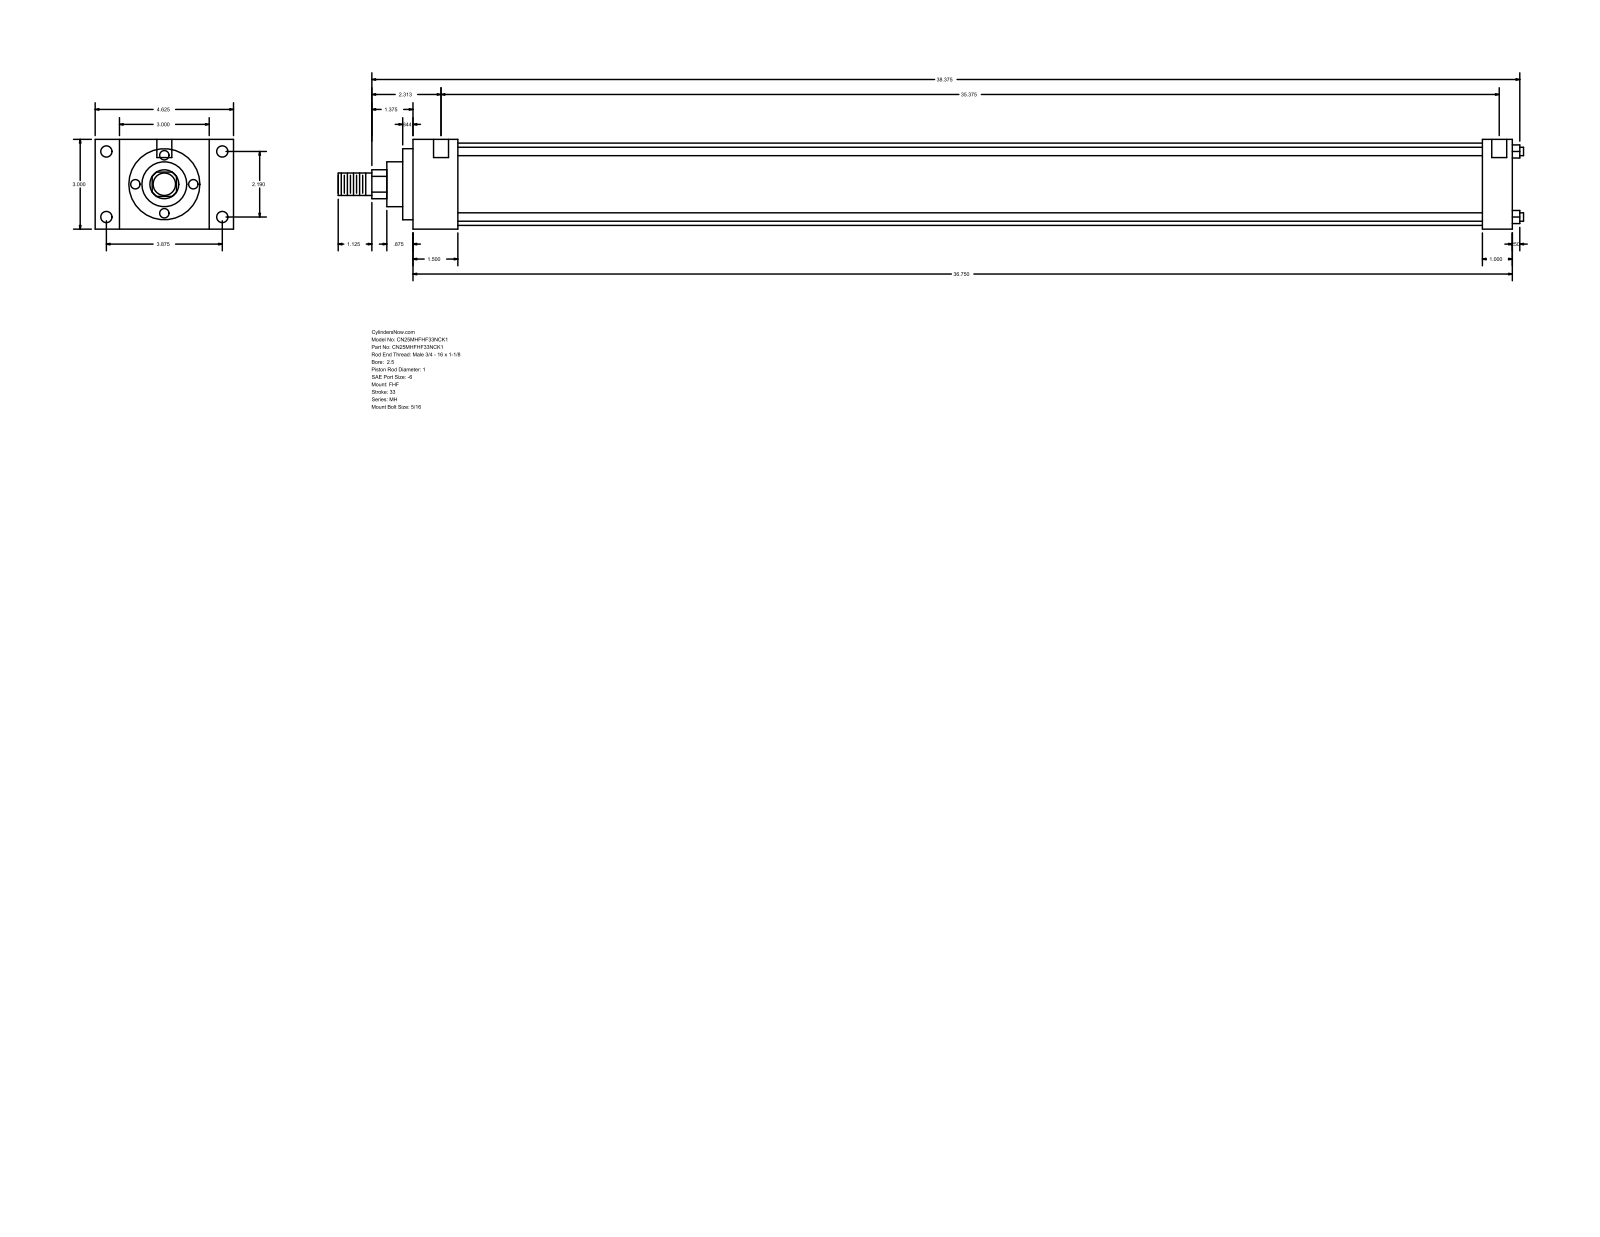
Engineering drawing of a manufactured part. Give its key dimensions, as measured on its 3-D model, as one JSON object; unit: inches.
{"part_name": "MH_FHF__0250_1", "step_written_by": "GSSL Pune (CONFIG_CONTROL_DESIGN)", "units": "inches", "bodies": {"solids": 0, "faces": 90, "planar": 61, "cylindrical": 29, "other": 0}, "overall_size": [39.625, 4.625, 3], "round_holes": [[0.219, 4], [0.375, 4], [0.5, 2]], "round_bosses_or_shafts": [[0.281, 4], [2.75, 1], [2.375, 1], [1.5, 1], [1, 1], [0.75, 1]], "partial_cylinders_radius": [[0.484, 1]], "face_to_face_distances": [3, 36.75, 1.5, 35.25, 0.813, 3.813, 4.625, 35.75, 34.25, 1], "hole_center_spacings": [2.19, 3.875, 4.451, 35.687, 0.125, 0.187, 35.375, 35.5]}
